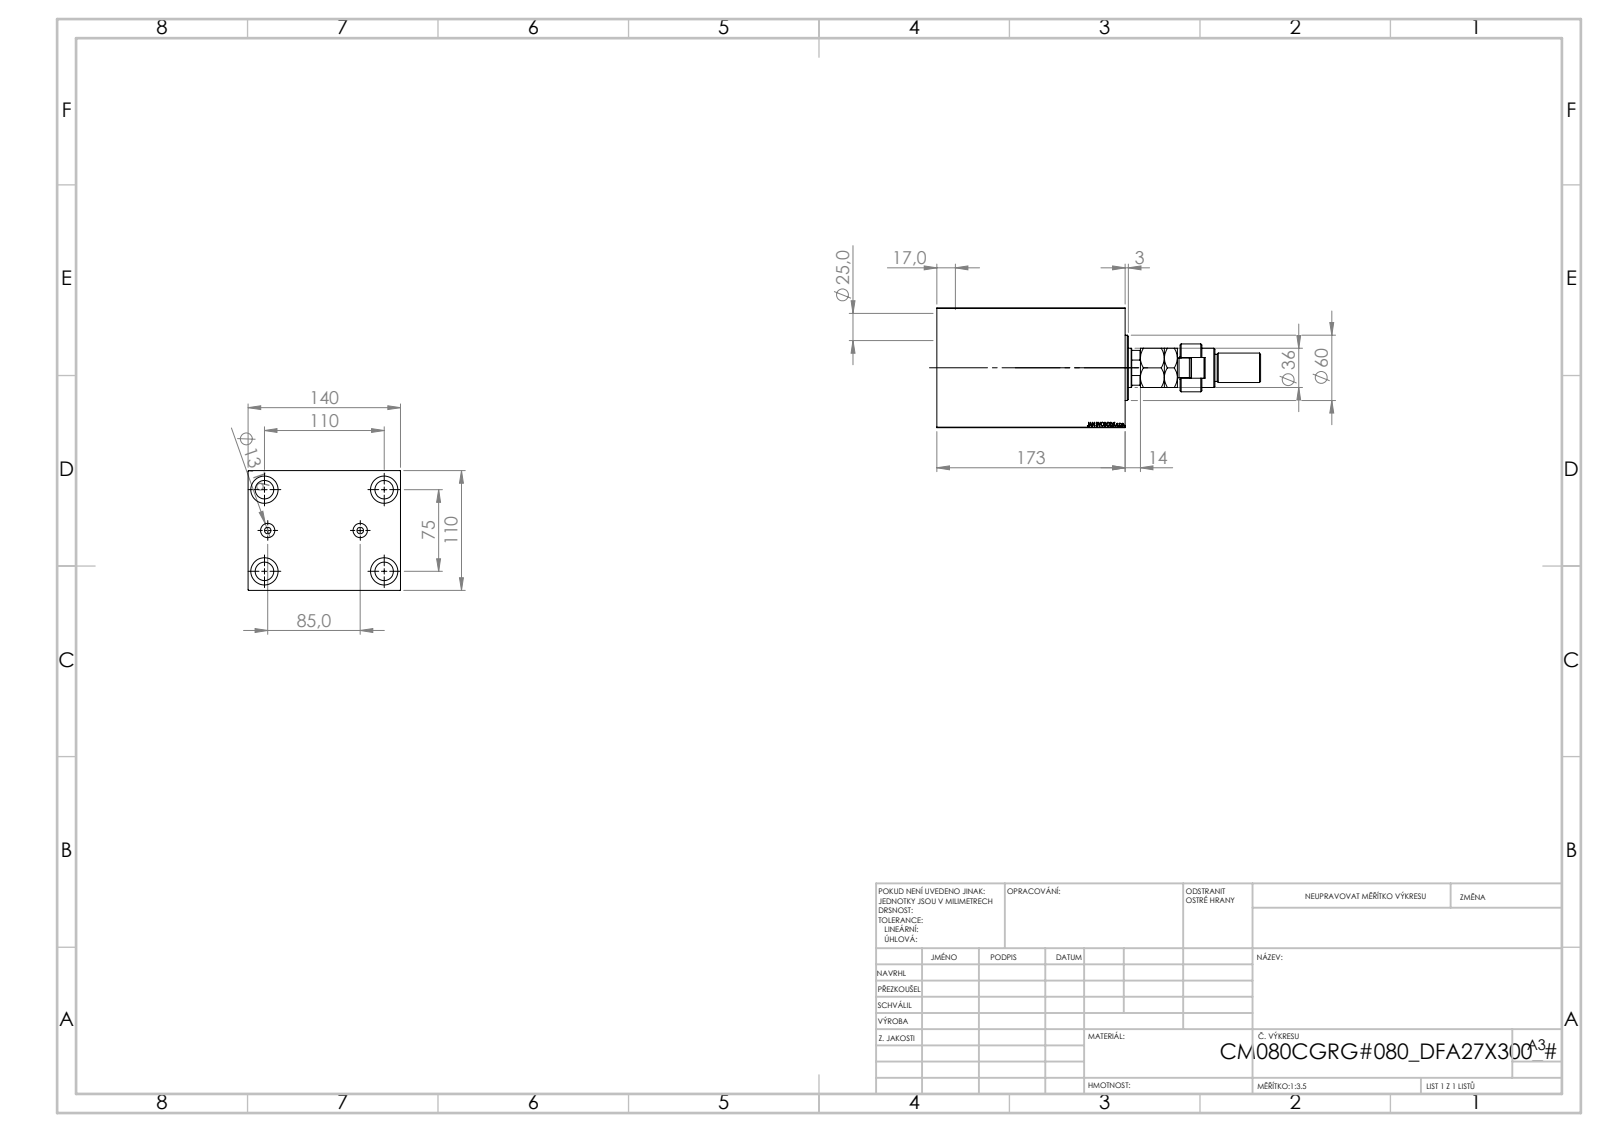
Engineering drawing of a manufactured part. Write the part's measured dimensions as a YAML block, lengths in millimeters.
part_name: "V450CM_VC_B; MFA; V450CM_C_VCP; V450CM_C_Body (+1 more)"
step_written_by: "SolidWorks 2019 (CONFIG_CONTROL_DESIGN)"
units: millimeters
bodies: {solids: 5, faces: 948, planar: 439, cylindrical: 71, other: 438}
overall_size: [297.5, 140, 110]
volume: 2239000
surface_area: 280491
round_holes:
  - {diameter: 17, count: 4}
  - {diameter: 25, count: 4}
  - {diameter: 6, count: 2}
  - {diameter: 13.16, count: 2}
  - {diameter: 25.5, count: 1}
  - {diameter: 39.5, count: 1}
  - {diameter: 80, count: 1}
  - {diameter: 82, count: 1}
  - {diameter: 87, count: 1}
round_bosses_or_shafts:
  - {diameter: 60, count: 1}
  - {diameter: 44, count: 1}
  - {diameter: 36, count: 1}
  - {diameter: 28, count: 1}
  - {diameter: 27, count: 1}
  - {diameter: 25, count: 1}
  - {diameter: 18, count: 1}
partial_cylinders:
  - {radius: 9.5, count: 1}
  - {radius: 15, count: 1}
  - {radius: 17.5, count: 1}
face_to_face_distances: [110, 140, 173, 152, 21, 37.3, 114.7, 135.7, 117.3, 80]
hole_center_spacings: [39.53, 66.57, 104.46, 42.5, 75, 110, 133.14, 85]
